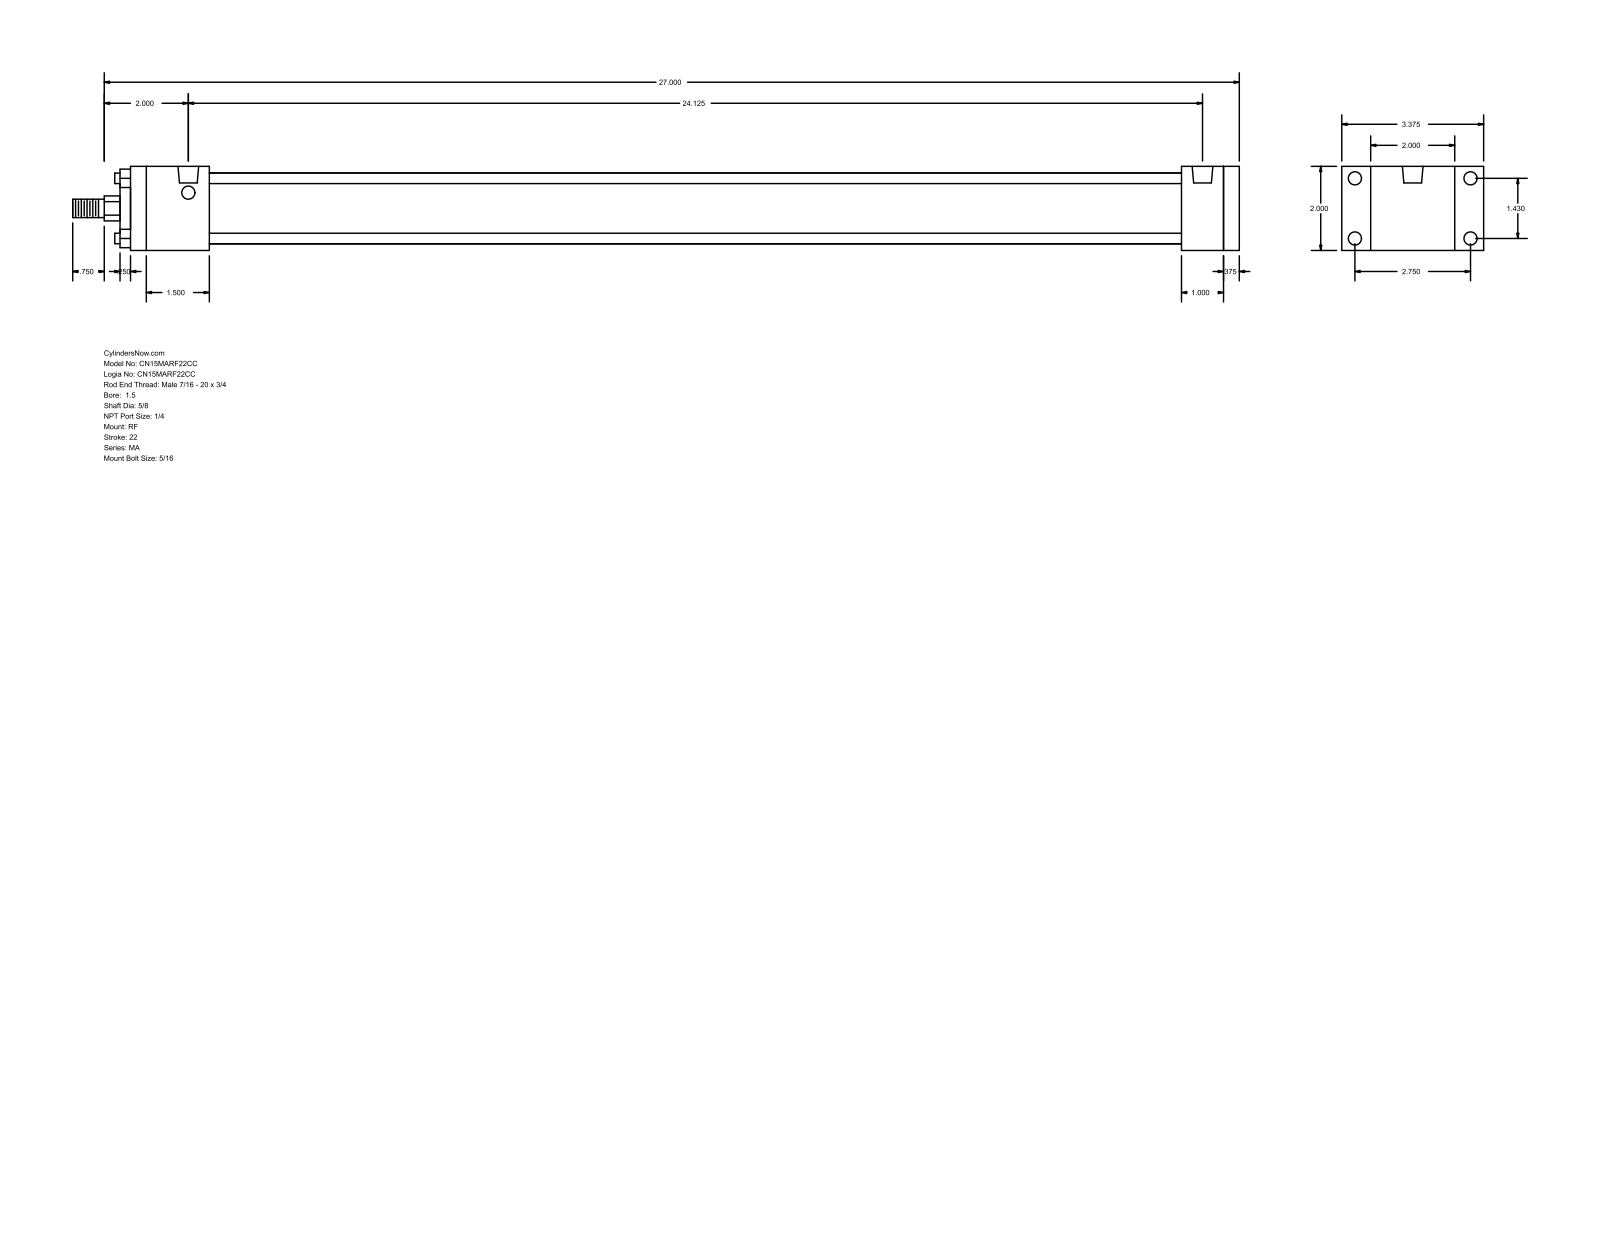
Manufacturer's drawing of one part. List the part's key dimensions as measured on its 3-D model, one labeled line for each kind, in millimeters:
Part name (STEP PRODUCT): MA_RF__0150_0.625
STEP written by: GSSL Pune (CONFIG_CONTROL_DESIGN)
Units: millimetres
Bodies: 0 solids, 92 faces (64 planar, 28 cylindrical, 0 other)
Overall size (bounding box): 704.85 × 85.72 × 50.8
Round holes (diameter × count): ⌀7.94 ×8, ⌀12.49 ×2
Round bosses / shafts (diameter × count): ⌀6.35 ×4, ⌀42.93 ×1, ⌀28.57 ×1, ⌀15.88 ×1, ⌀11.11 ×1
Partial cylindrical surfaces — rounded edges, fillets, slot ends (radius × count): R7.54 ×1
Main face-to-face distances: 50.8, 9.53, 669.92, 660.39, 635, 25.39, 34.92, 47.62, 587.38, 612.77
Hole centre spacings: 36.32, 69.84, 78.72, 612.78
